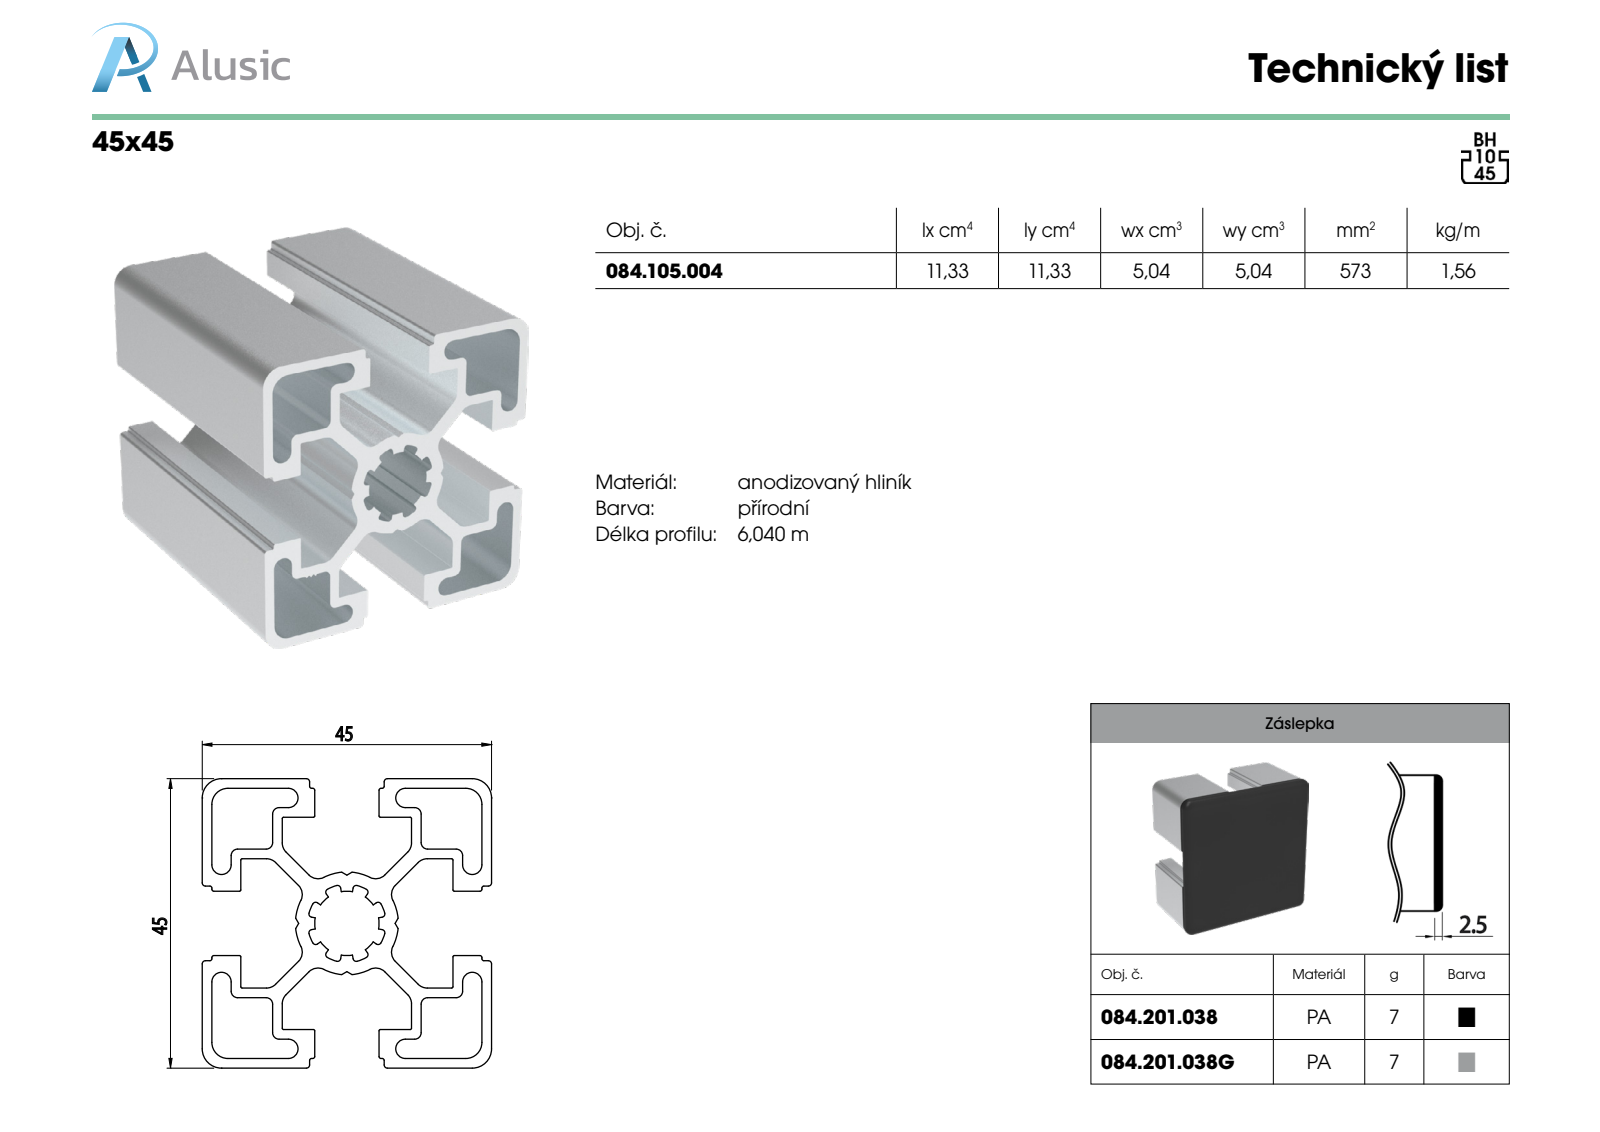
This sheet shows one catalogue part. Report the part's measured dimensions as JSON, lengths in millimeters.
{"part_name": "084.105.004", "step_written_by": "SolidWorks 2018 (AUTOMOTIVE_DESIGN)", "units": "millimeters", "bodies": {"solids": 1, "faces": 248, "planar": 115, "cylindrical": 133, "other": 0}, "overall_size": [100, 45, 45], "volume_mm3": 57267, "surface_area_mm2": 60962, "partial_cylinders_radius": [[0.5, 24], [0.2, 16], [0.3, 16], [2, 16], [1, 12], [1.5, 8], [2.5, 4], [3, 4]], "face_to_face_distances": [1.5, 43.5, 10.95, 32.55, 45, 4.5, 39, 28.05, 6.45, 42]}
